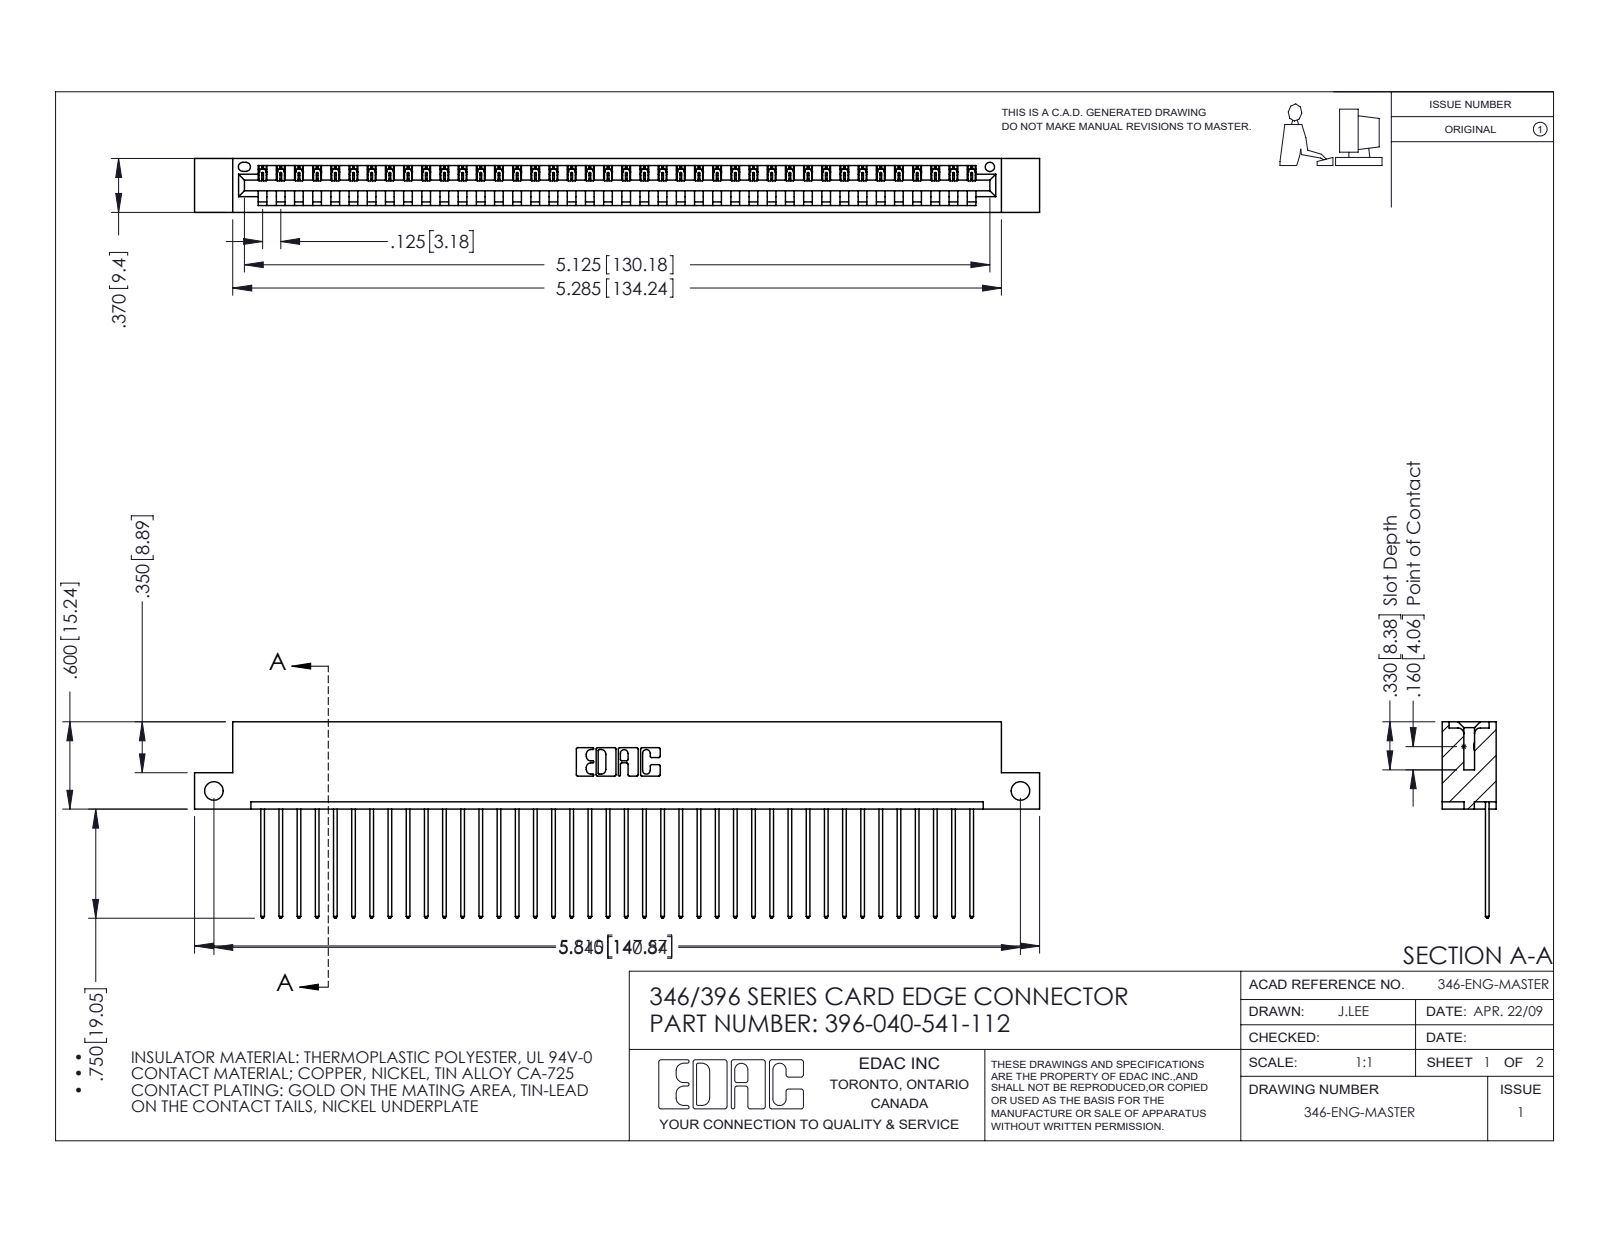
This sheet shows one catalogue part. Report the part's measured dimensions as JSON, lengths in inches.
{"part_name": "396-040-541-112; 346 Part_Flush Mounting Lugs - Side Mount; 345-292-001_345-293-141", "step_written_by": "SolidWorks 2016 (CONFIG_CONTROL_DESIGN)", "units": "inches", "bodies": {"solids": 41, "faces": 2442, "planar": 1676, "cylindrical": 766, "other": 0}, "overall_size": [5.81, 1.35, 0.37], "volume_in3": 0.864, "surface_area_in2": 28.39, "round_holes": [[0.128, 2], [0.064, 1]], "partial_cylinders_radius": [[0.006, 80], [0.01, 80], [0.01, 22], [0.007, 6], [0.031, 6], [0.026, 3], [0.031, 2], [0.04, 2]], "face_to_face_distances": [0.048, 0.322, 0.37, 0.25, 0.072, 0.298, 0.025, 0.148, 0.222, 0.1], "hole_center_spacings": [5.545]}
